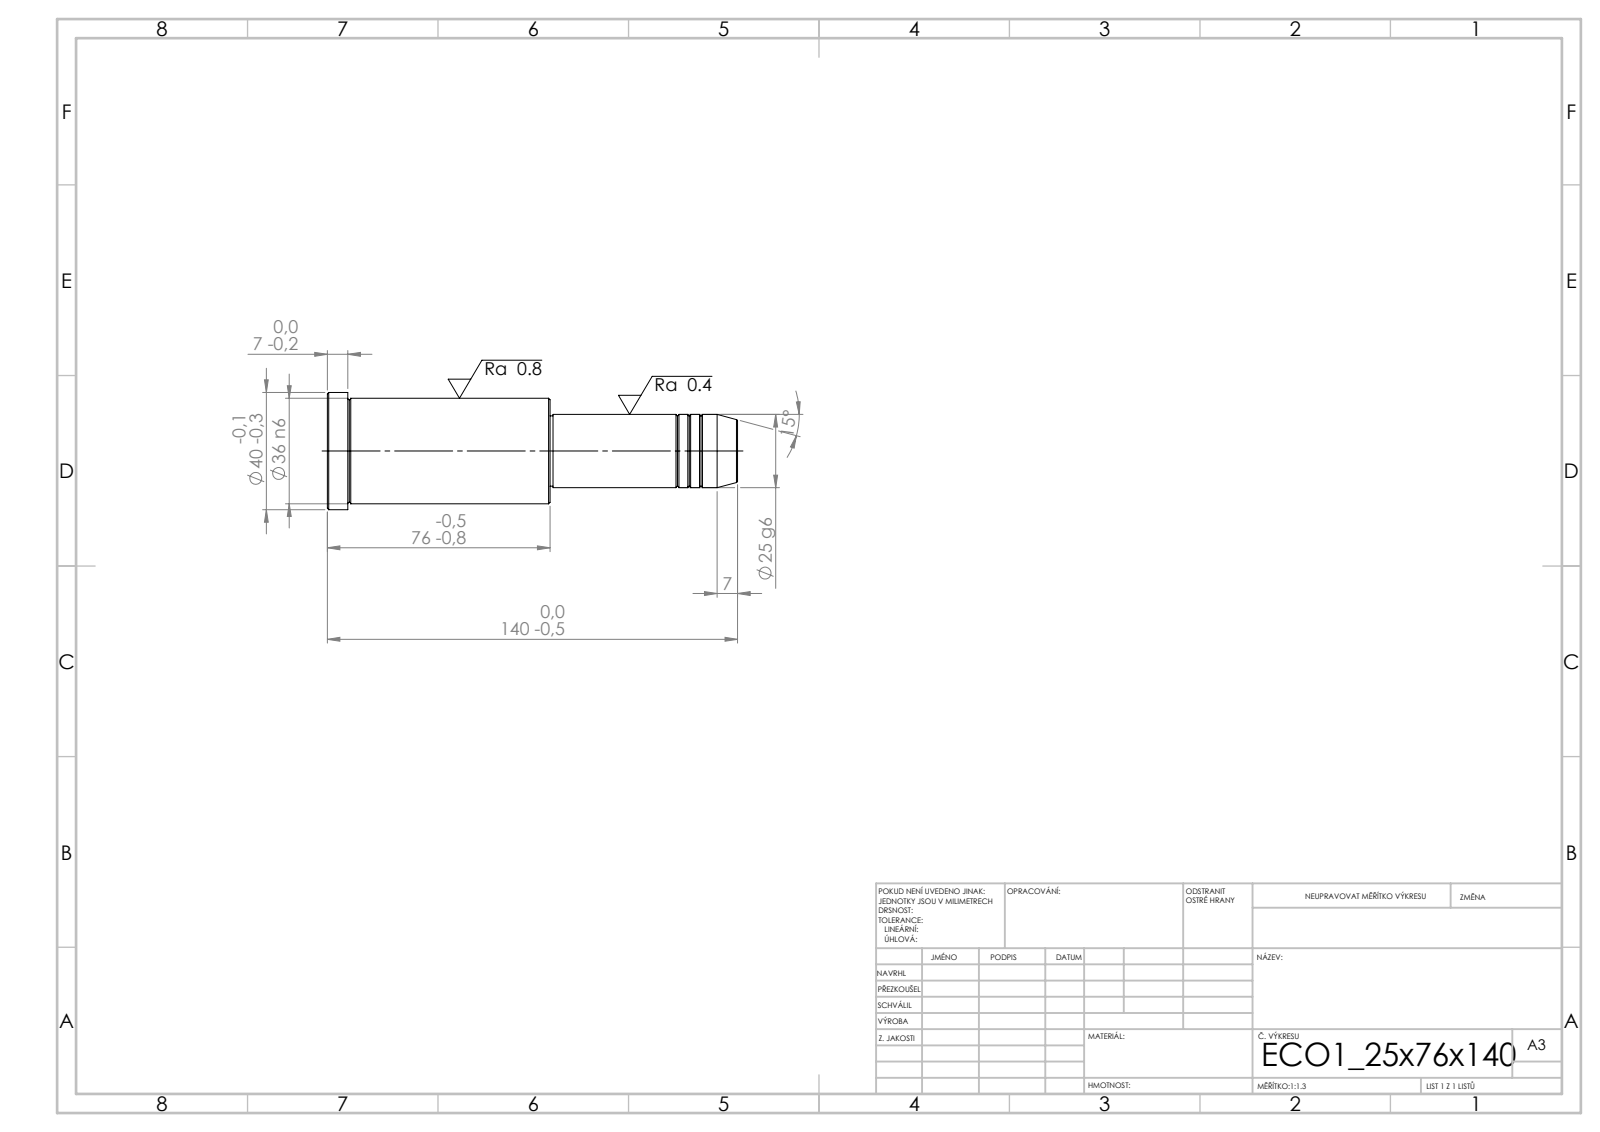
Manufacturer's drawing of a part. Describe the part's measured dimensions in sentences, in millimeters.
Its 3-D file was written by "SolidWorks 2019 (CONFIG_CONTROL_DESIGN)". It is 1 solid with 43 faces: 5 planar, 14 cylindrical and 24 other. Overall it measures 140 by 40 by 40 millimeters. Its volume is 109 751 cubic millimeters and its surface area 16 246 square millimeters. Round bosses or shafts: 1 of diameter 40, 1 of diameter 36, 1 of diameter 25, 1 of diameter 24. The main face-to-face distances are 76, 64, 140, 133, 69, 7, 63, 1, 70, 77.
